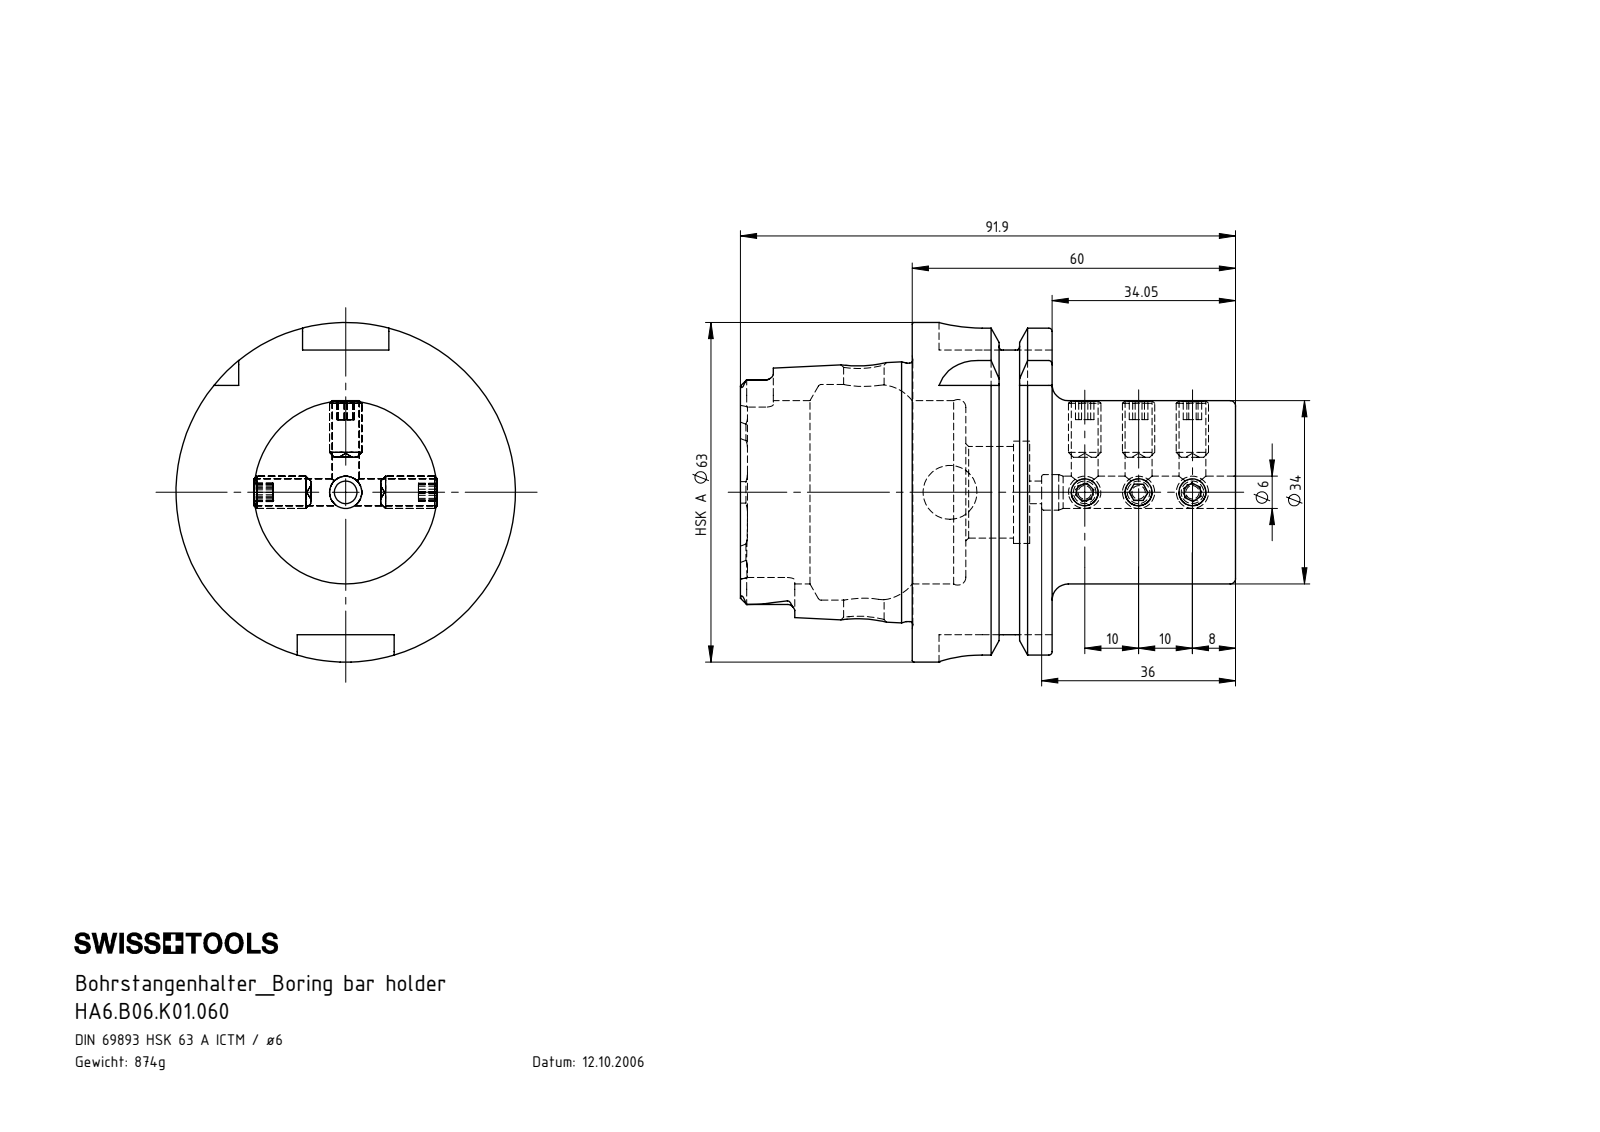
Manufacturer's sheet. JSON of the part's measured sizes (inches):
{"part_name": "HA6.B06.K01.060; HA6-B06.K01.060_B_Fertigbearbeitung; ISO 4026 - M6 x 10_PreviewCfg", "step_written_by": "SolidWorks 2017 (AUTOMOTIVE_DESIGN)", "units": "inches", "bodies": {"solids": 10, "faces": 331, "planar": 128, "cylindrical": 88, "other": 115}, "overall_size": [3.618, 2.48, 2.48], "volume_in3": 6.784, "surface_area_in2": 47.12, "round_holes": [[0.197, 6], [0.165, 1], [0.236, 1], [0.26, 1], [0.295, 1], [0.394, 1], [0.669, 1], [0.748, 1], [1.339, 1], [1.575, 1]], "round_bosses_or_shafts": [[0.236, 6], [2.48, 1], [2.163, 1], [1.887, 1]], "partial_cylinders_radius": [[0.055, 6], [0.113, 4], [0.315, 4]], "face_to_face_distances": [1.022, 2.362, 1.341, 0.63, 0.392, 1.97, 1.256, 1.648, 2.278, 3.618], "hole_center_spacings": [0.394, 0.787, 0.984, 1.378, 1.614, 1.772, 2.008, 2.402]}
